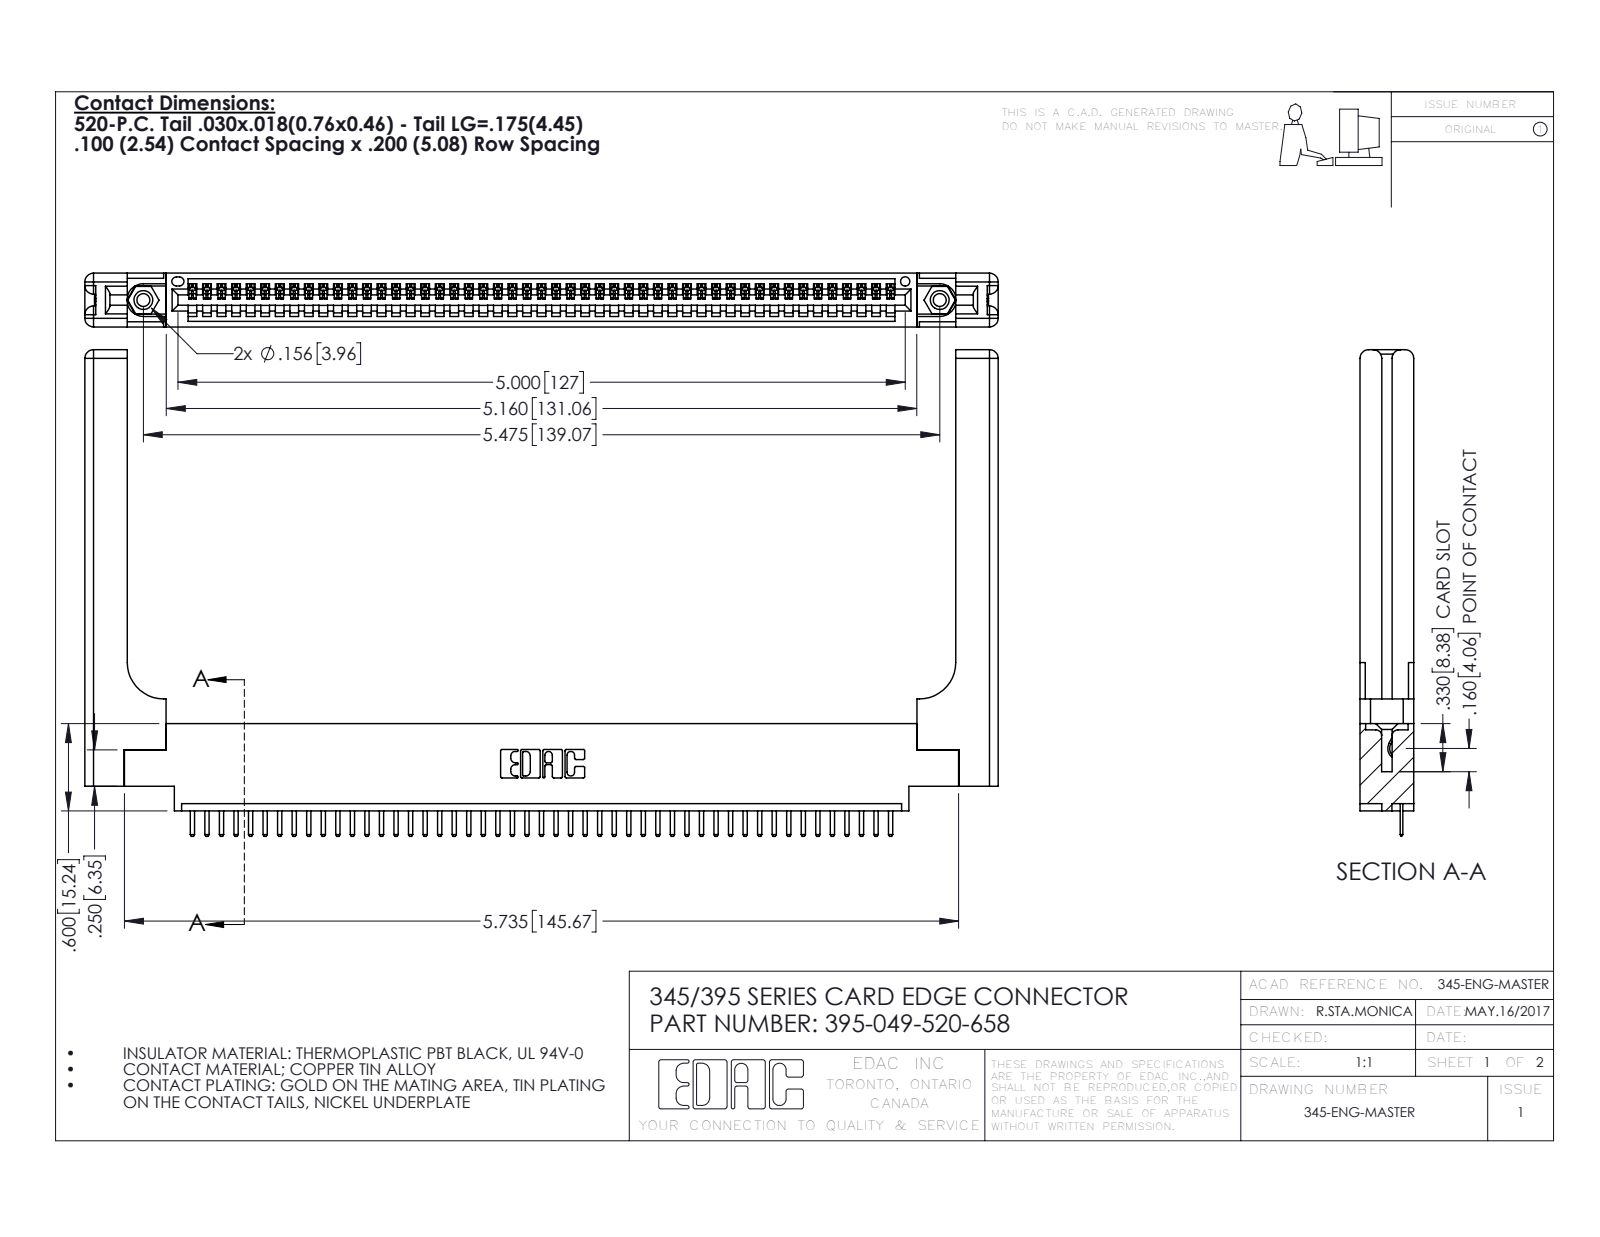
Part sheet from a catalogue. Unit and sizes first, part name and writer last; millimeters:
Units: millimetres
Overall size (bounding box): 159.5 × 85 × 9.4
Round holes (diameter × count): ⌀2.3 ×2, ⌀3.2 ×2, ⌀4 ×2, ⌀1.6 ×1
Round bosses / shafts (diameter × count): ⌀3.9 ×2
Partial cylindrical surfaces — rounded edges, fillets, slot ends (radius × count): R0.3 ×100, R0.2 ×98, R0.3 ×22, R1.5 ×16, R0.2 ×6, R0.8 ×6, R0.7 ×3, R0.8 ×2
Main face-to-face distances: 9.4, 1.8, 7.6, 2.5, 6.9, 0.6, 5.1, 5.7, 3.8, 3.8
Hole centre spacings: 6.9, 133.1, 139.1
Volume: 23 450 mm³ · Surface area: 24 940 mm²
Bodies: 54 solids, 3424 faces (2290 planar, 1074 cylindrical, 60 other)
Part name (STEP PRODUCT): 345-292-001_345-293-120; 345-220-058_345-220-058; 345 Part_0.170 Offset - 0.156 Dia-TH; 395-049-520-658 (+1 more)
STEP written by: SolidWorks 2016 (CONFIG_CONTROL_DESIGN)
